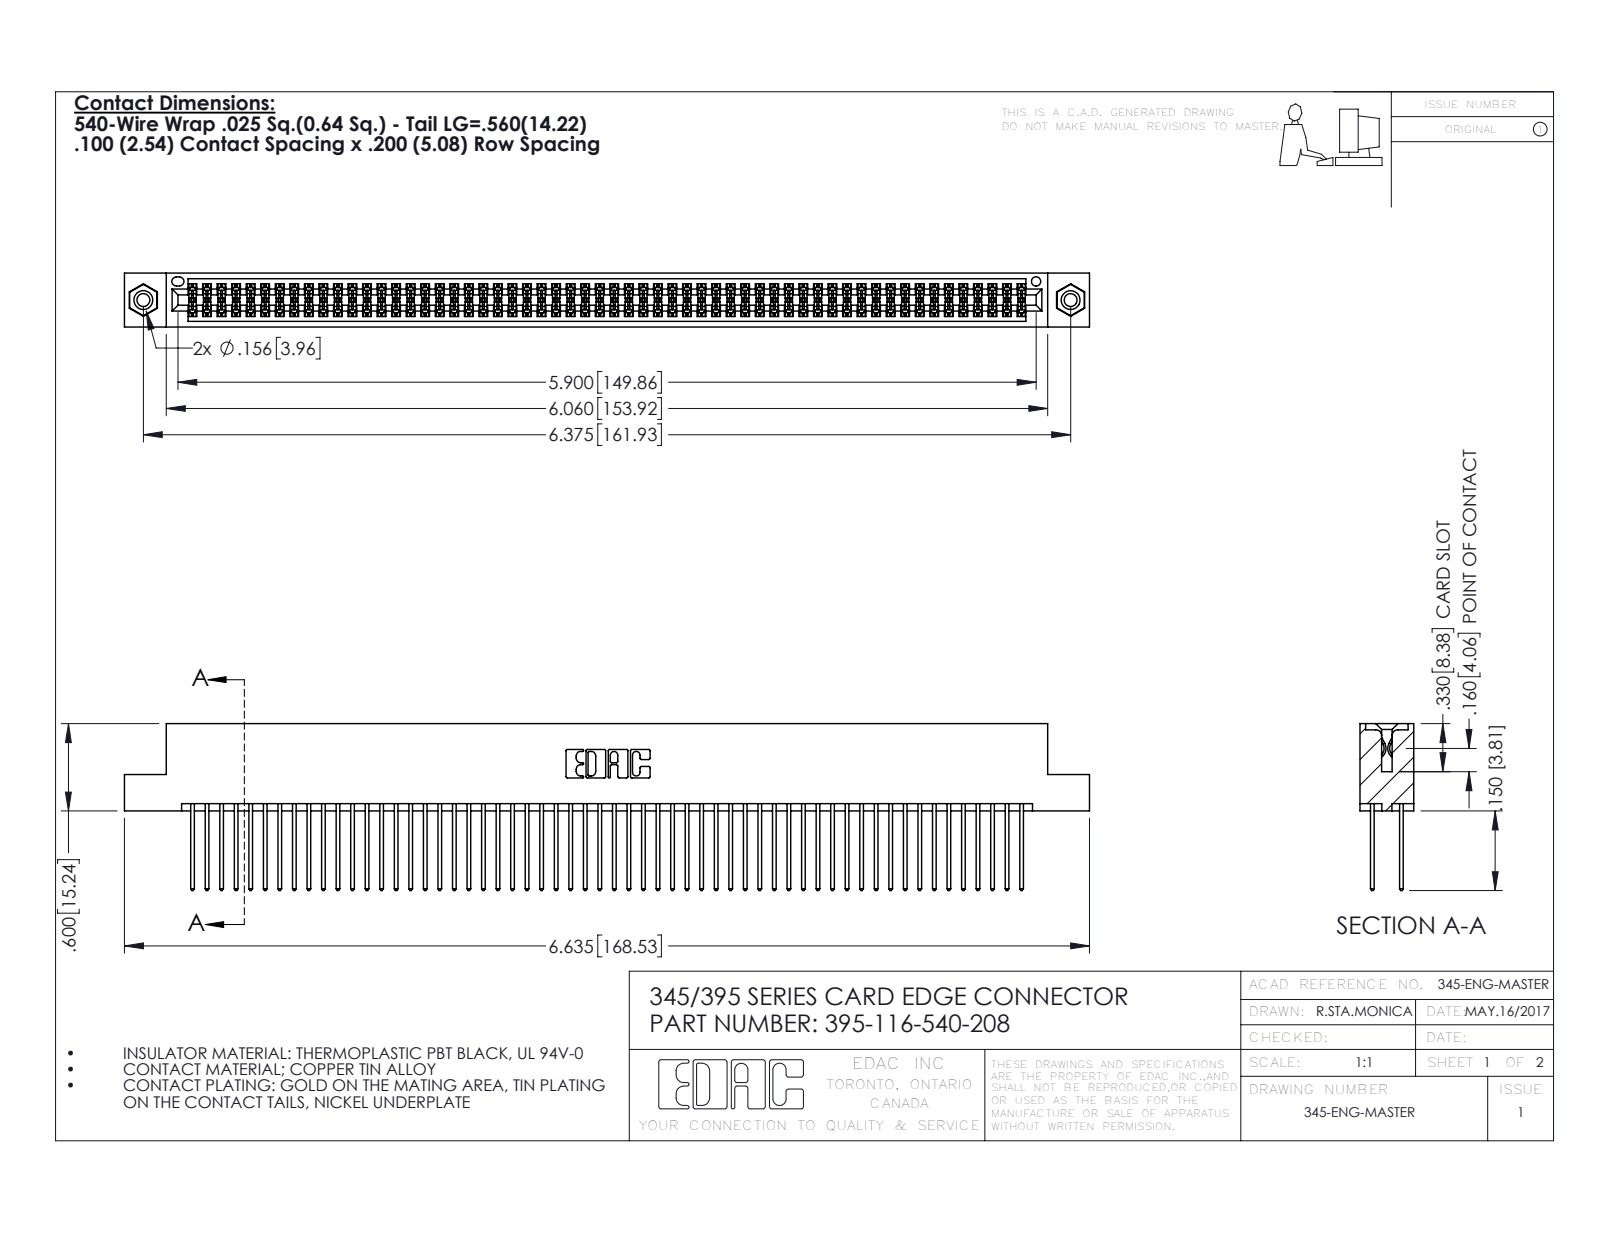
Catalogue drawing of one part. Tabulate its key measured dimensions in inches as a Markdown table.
| quantity | value |
| --- | --- |
| part name | 395-116-540-208; 345-292-001_345-293-140; 345 Part_Flush Mounting Lugs - 0.156 Dia-TI; 345-250-001_345-250-003-102 |
| STEP written by | SolidWorks 2016 (CONFIG_CONTROL_DESIGN) |
| units | inches |
| bodies | 119 solids, 5986 faces (3940 planar, 2030 cylindrical, 16 other) |
| overall size | 6.635 × 1.147 × 0.37 |
| volume | 1.035 in³ |
| surface area | 42.51 in² |
| round holes (diameter × count) | 0.089 × 2, 0.125 × 2, 0.156 × 2, 0.064 × 1 |
| round bosses / shafts (diameter × count) | 0.155 × 2 |
| partial cylindrical surfaces (radius × count) | 0.006 × 174, 0.01 × 116, 0.01 × 22, 0.007 × 6, 0.031 × 6, 0.026 × 3, 0.014 × 2, 0.019 × 2 |
| main face-to-face distances | 0.072, 0.298, 0.2, 0.098, 0.272, 0.025, 0.37, 0.225, 0.175, 0.149 |
| hole center spacings | 0.27, 6.139, 6.375 |
